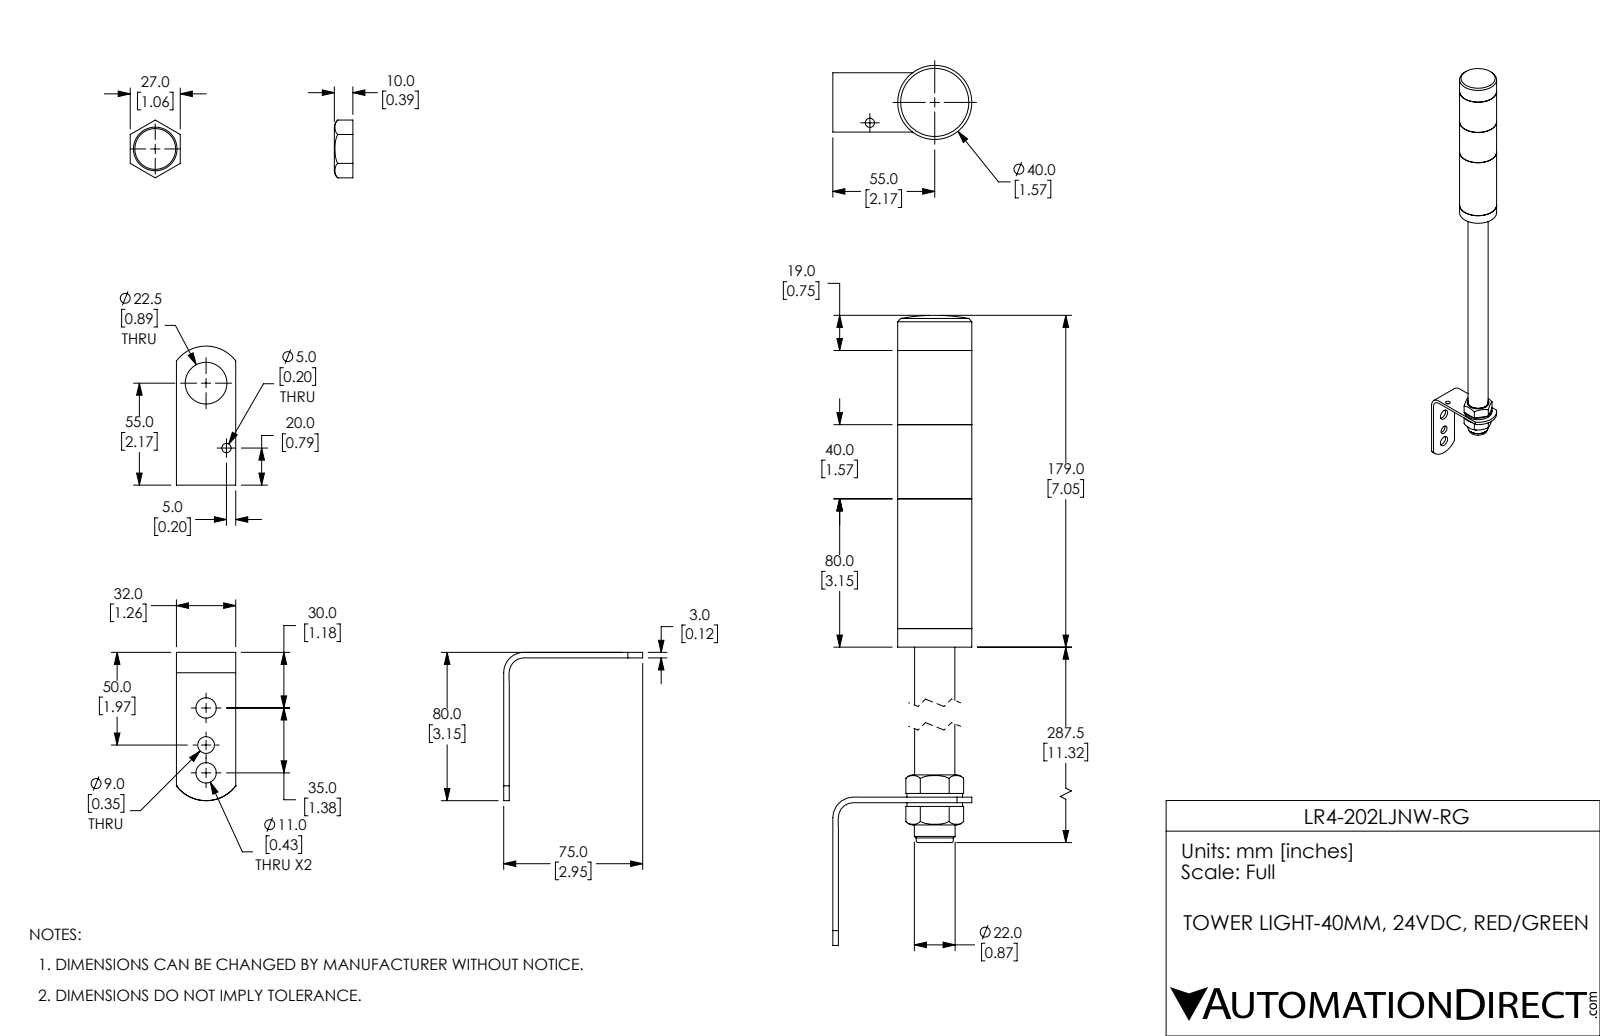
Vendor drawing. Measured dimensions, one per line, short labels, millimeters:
name: LR4-202LJNW-RG
written by: SolidWorks 2017 (AUTOMOTIVE_DESIGN)
unit: mm
bodies: 11 solids, 146 faces (52 planar, 79 cylindrical, 15 other)
size: 522 × 75 × 40
volume: 289 700 mm³; area: 102 200 mm²
holes: 2× ⌀3.2, 2× ⌀11, 1× ⌀5, 1× ⌀7.7, 1× ⌀9, 1× ⌀17.7, 1× ⌀22, 1× ⌀22.5, 1× ⌀27.6, 1× ⌀34.7, 1× ⌀35.2, 1× ⌀35.3
bosses: 1× ⌀40, 1× ⌀30, 1× ⌀21.7
rounds: 1× R20
face distances: 40, 80, 66, 106, 146, 90.3, 5, 10.3, 278, 24.3
hole spacings: 7.2, 14.4, 15, 20, 29.9, 35, 36.7, 43.6
